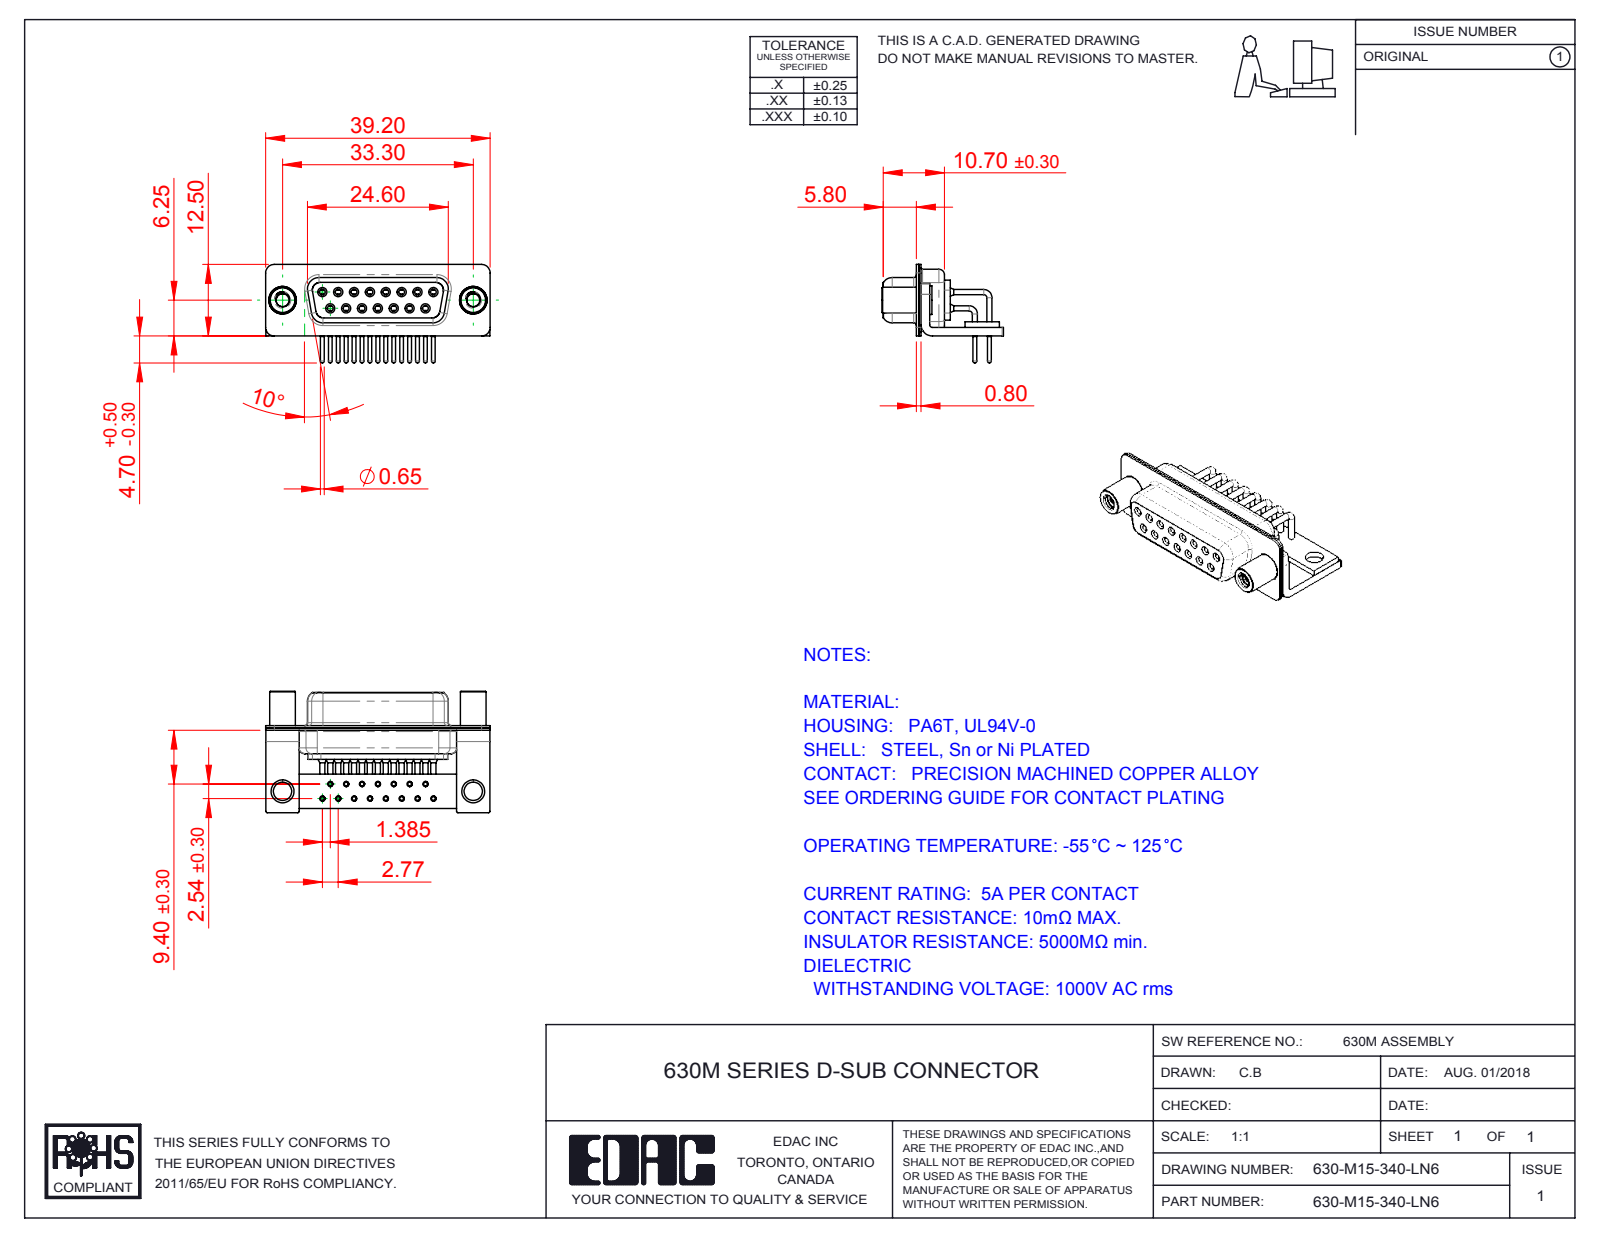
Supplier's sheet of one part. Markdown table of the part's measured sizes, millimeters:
| quantity | value |
| --- | --- |
| part name | 630M Shell Rear_15 Contacts; 630M Stabilizer Bracket; 630M Contact Row 2; 630-M15-340-LN6 (+5 more) |
| STEP written by | SolidWorks 2016 (CONFIG_CONTROL_DESIGN) |
| units | millimeters |
| bodies | 23 solids, 1204 faces (320 planar, 576 cylindrical, 308 other) |
| overall size | 39.2 × 21.2 × 17.2 |
| volume | 3 171 mm³ |
| surface area | 8 035 mm² |
| round holes (diameter × count) | 0.9 × 15, 1 × 15, 1.1 × 15, 1.7 × 15, 1.8 × 15, 2 × 15, 2.26 × 2, 3.2 × 2, 4 × 2, 4.8 × 2 |
| round bosses / shafts (diameter × count) | 0.9 × 27, 1.6 × 15, 1.5 × 15, 0.65 × 15, 5 × 2, 4.9 × 2, 4.5 × 2 |
| partial cylindrical surfaces (radius × count) | 0.25 × 16, 1.5 × 16, 2 × 13, 1.35 × 8, 1.6 × 8, 0.5 × 5, 0.6 × 4, 0.65 × 4 |
| main face-to-face distances | 0.4, 2.3, 1.9, 0.8, 1.5, 9.35, 1, 1.45, 8.95, 0.85 |
| hole center spacings | 2.77, 5.54, 8.31, 3.16, 4.87, 11.08, 2.89, 7.37 |
